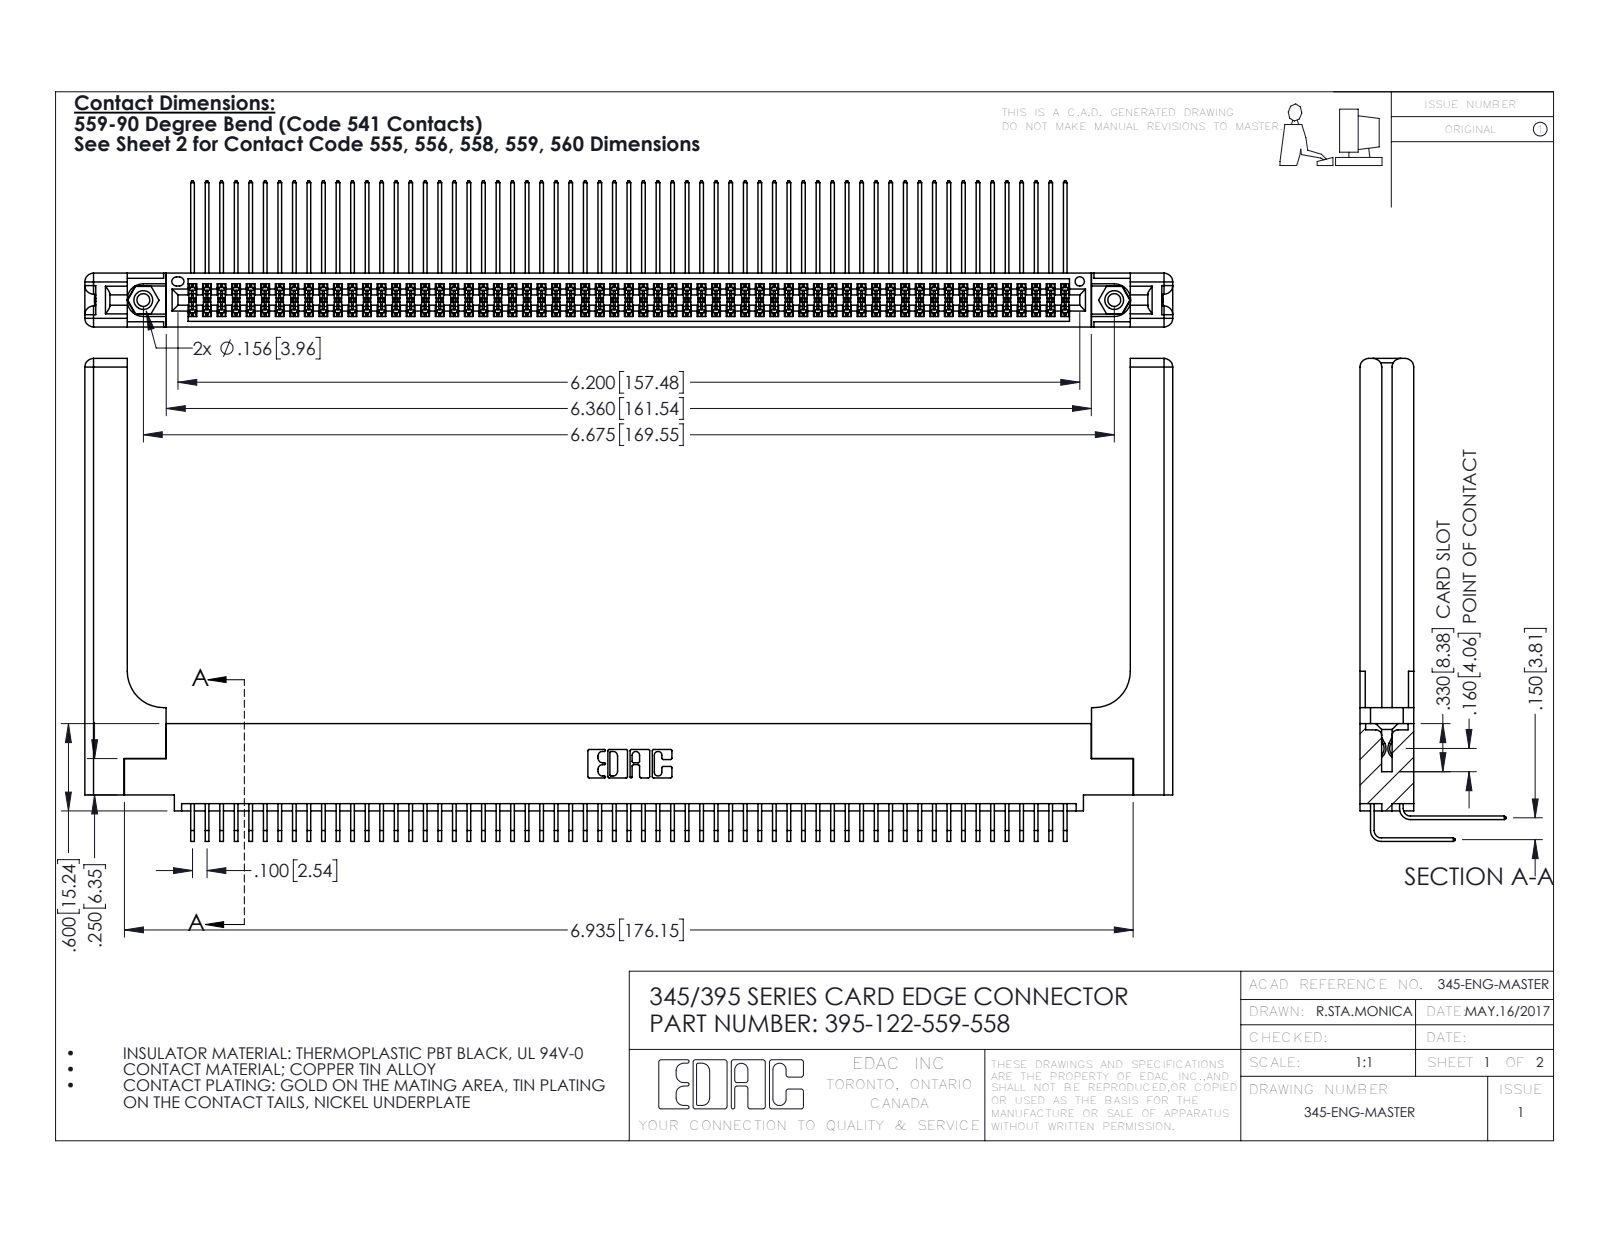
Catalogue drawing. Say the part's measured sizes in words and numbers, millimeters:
The part is named "345-250-001_345-250-001-102; 345-292-001_558 559 Tail - 1; 395-122-559-558; 345-220-058_345-220-058 (+2 more)". Its 3-D file was written by "SolidWorks 2016 (CONFIG_CONTROL_DESIGN)". It is 127 solids with 6730 faces: 4502 planar, 2168 cylindrical and 60 other. Overall it measures 190 by 84.3 by 25.5 millimeters. Its volume is 27 740 cubic millimeters and its surface area 37 300 square millimeters. Round holes: 2 of diameter 2.3, 2 of diameter 3.2, 2 of diameter 4, 1 of diameter 1.6. Round bosses or shafts: 2 of diameter 3.9. Partial cylindrical surfaces (rounded edges, fillets, slot ends): 183 of radius 0.2, 22 of radius 0.3, 16 of radius 1.5, 6 of radius 0.2, 6 of radius 0.8, 3 of radius 0.7, 2 of radius 0.4, 2 of radius 0.5. The main face-to-face distances are 1.8, 7.6, 9.4, 2.5, 6.9, 0.6, 5.1, 5.7, 4.4, 3.8. The hole center spacings are 6.9, 163.6, 169.5.
